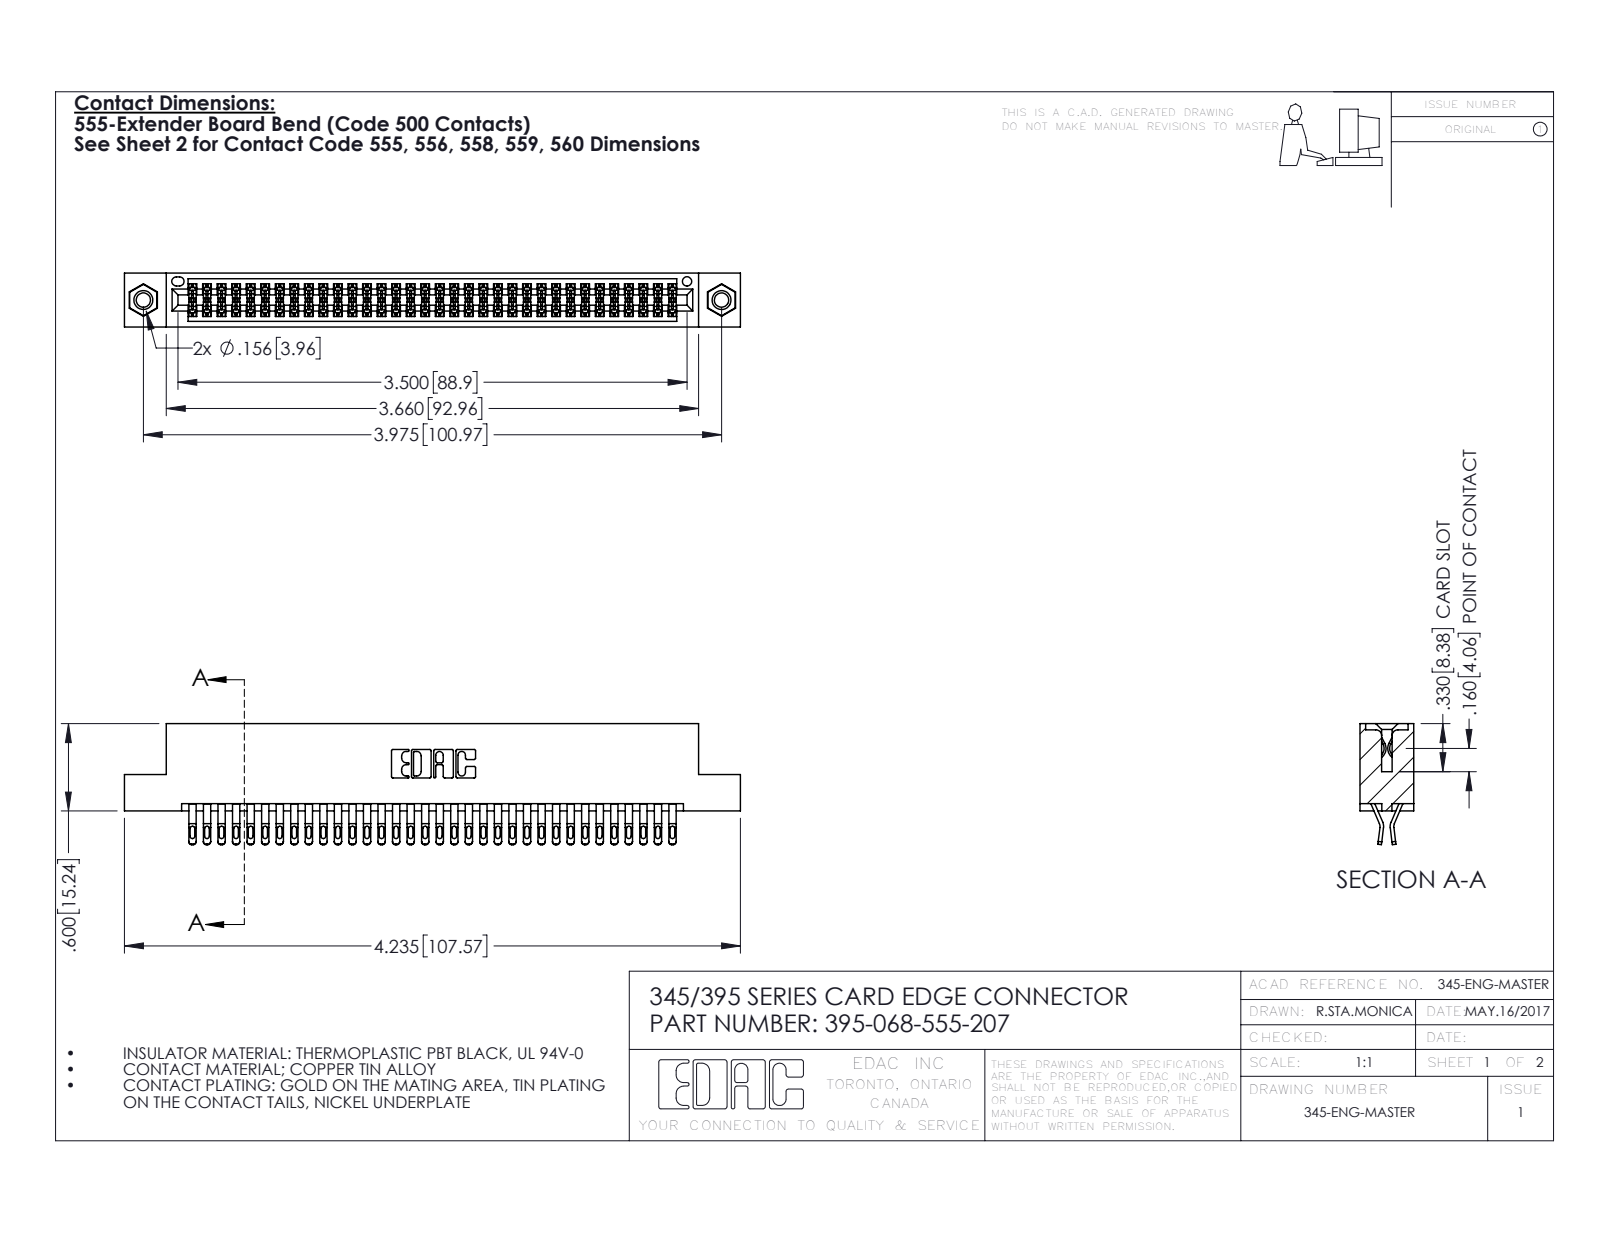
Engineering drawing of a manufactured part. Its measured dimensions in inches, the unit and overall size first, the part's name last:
Units: inches
Overall size (bounding box): 4.235 × 0.832 × 0.37
Round holes (diameter × count): ⌀0.098 ×2, ⌀0.125 ×2, ⌀0.156 ×2, ⌀0.064 ×1
Round bosses / shafts (diameter × count): ⌀0.155 ×2
Partial cylindrical surfaces — rounded edges, fillets, slot ends (radius × count): R0.016 ×170, R0.02 ×136, R0.006 ×102, R0.01 ×22, R0.007 ×6, R0.031 ×6, R0.026 ×3, R0.01 ×2
Main face-to-face distances: 0.072, 0.298, 0.2, 0.37, 0.025, 0.098, 0.272, 0.225, 0.175, 0.149
Hole centre spacings: 0.27, 3.74, 3.975
Volume: 0.644 in³ · Surface area: 25.06 in²
Bodies: 71 solids, 3994 faces (2220 planar, 1758 cylindrical, 16 other)
Part name (STEP PRODUCT): 395-068-555-207; 345 Part_Flush Mounting Lugs - 0.156 Dia-TI; 345-250-001_345-250-005-103; 345-292-001_555 Tail
STEP written by: SolidWorks 2016 (CONFIG_CONTROL_DESIGN)
